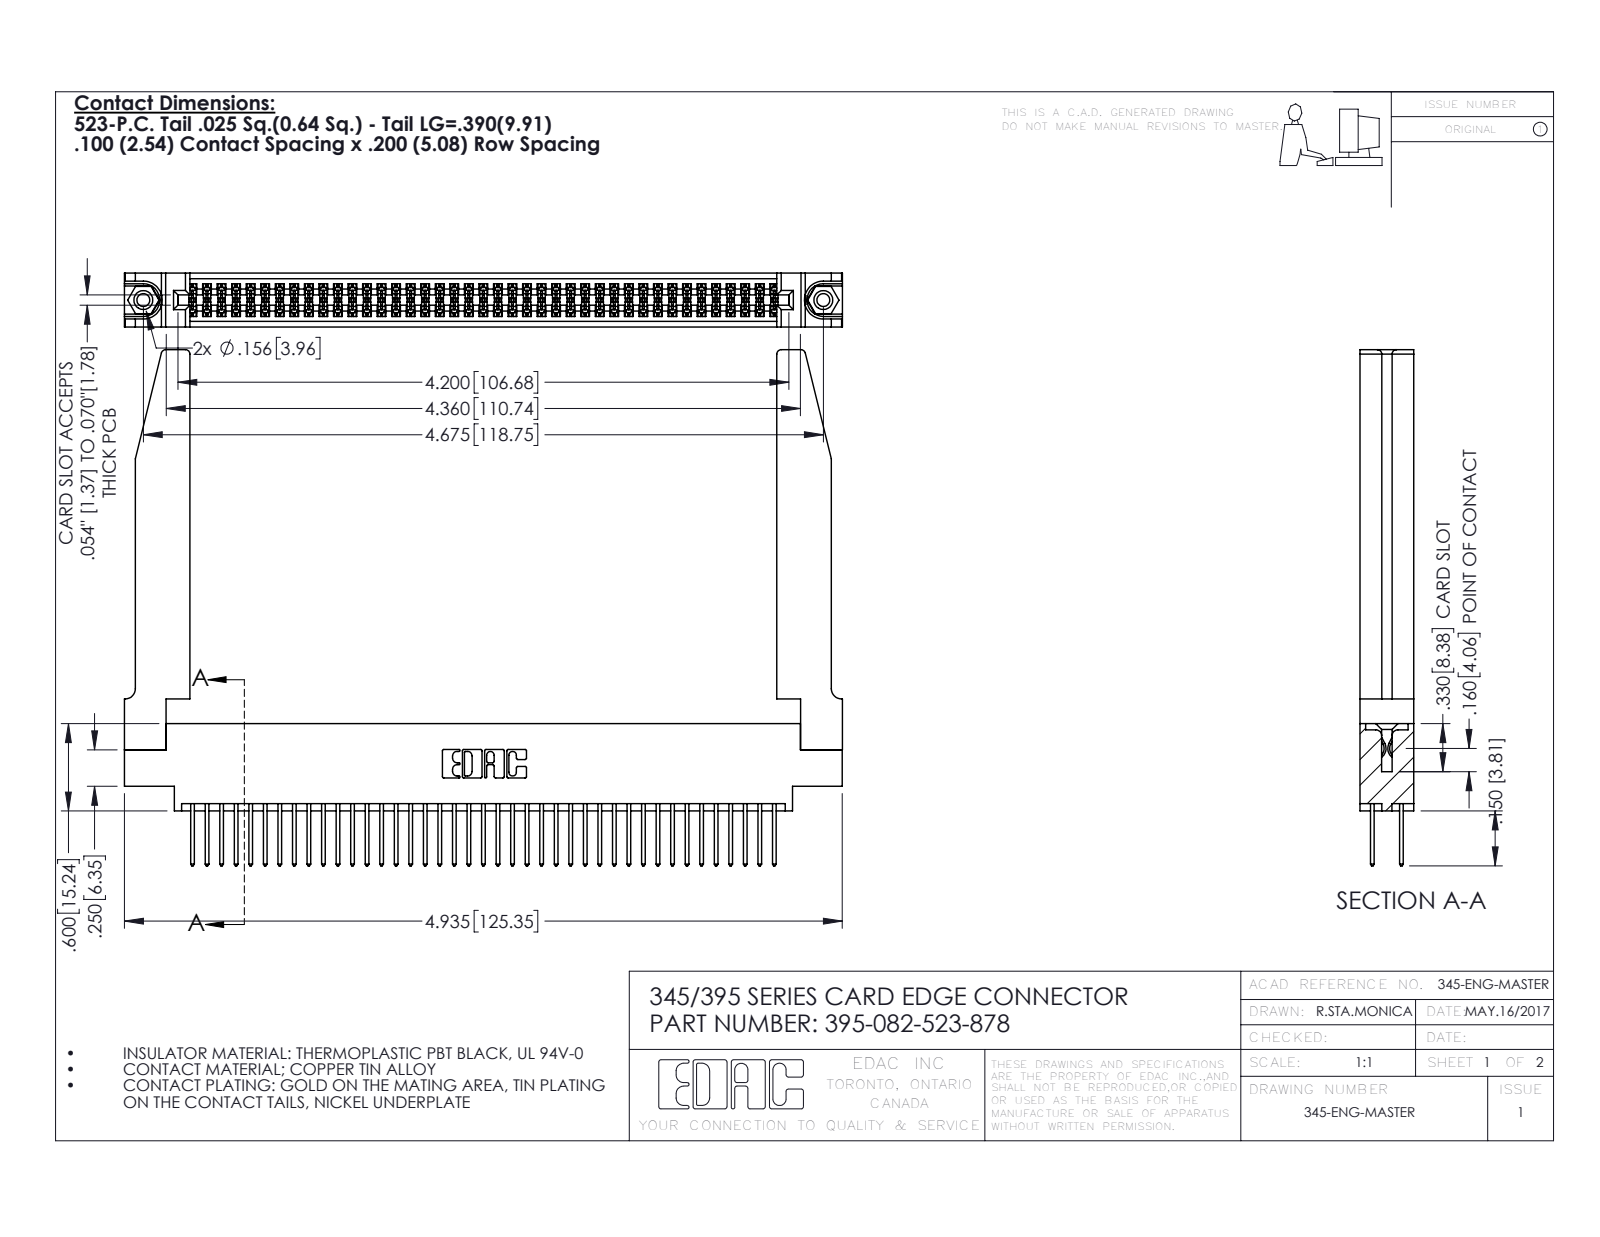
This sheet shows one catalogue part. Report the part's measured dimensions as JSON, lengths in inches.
{"part_name": "395-082-523-878; 345-292-001_345-293-123; 345 Part_0.170 Offset - 0.156 Dia-TH; 345-220-078_345-220-078 (+1 more)", "step_written_by": "SolidWorks 2016 (CONFIG_CONTROL_DESIGN)", "units": "inches", "bodies": {"solids": 87, "faces": 4464, "planar": 2932, "cylindrical": 1480, "other": 52}, "overall_size": [4.936, 3.547, 0.37], "volume_in3": 1.22, "surface_area_in2": 39.97, "round_holes": [[0.089, 2], [0.125, 2], [0.156, 2], [0.064, 1]], "round_bosses_or_shafts": [[0.155, 2]], "partial_cylinders_radius": [[0.006, 123], [0.01, 82], [0.01, 22], [0.03, 8], [0.007, 6], [0.031, 6], [0.026, 3], [0.014, 2]], "face_to_face_distances": [0.072, 0.37, 0.298, 0.2, 0.098, 0.272, 0.025, 0.225, 0.175, 0.148], "hole_center_spacings": [0.27, 4.439, 4.675]}
